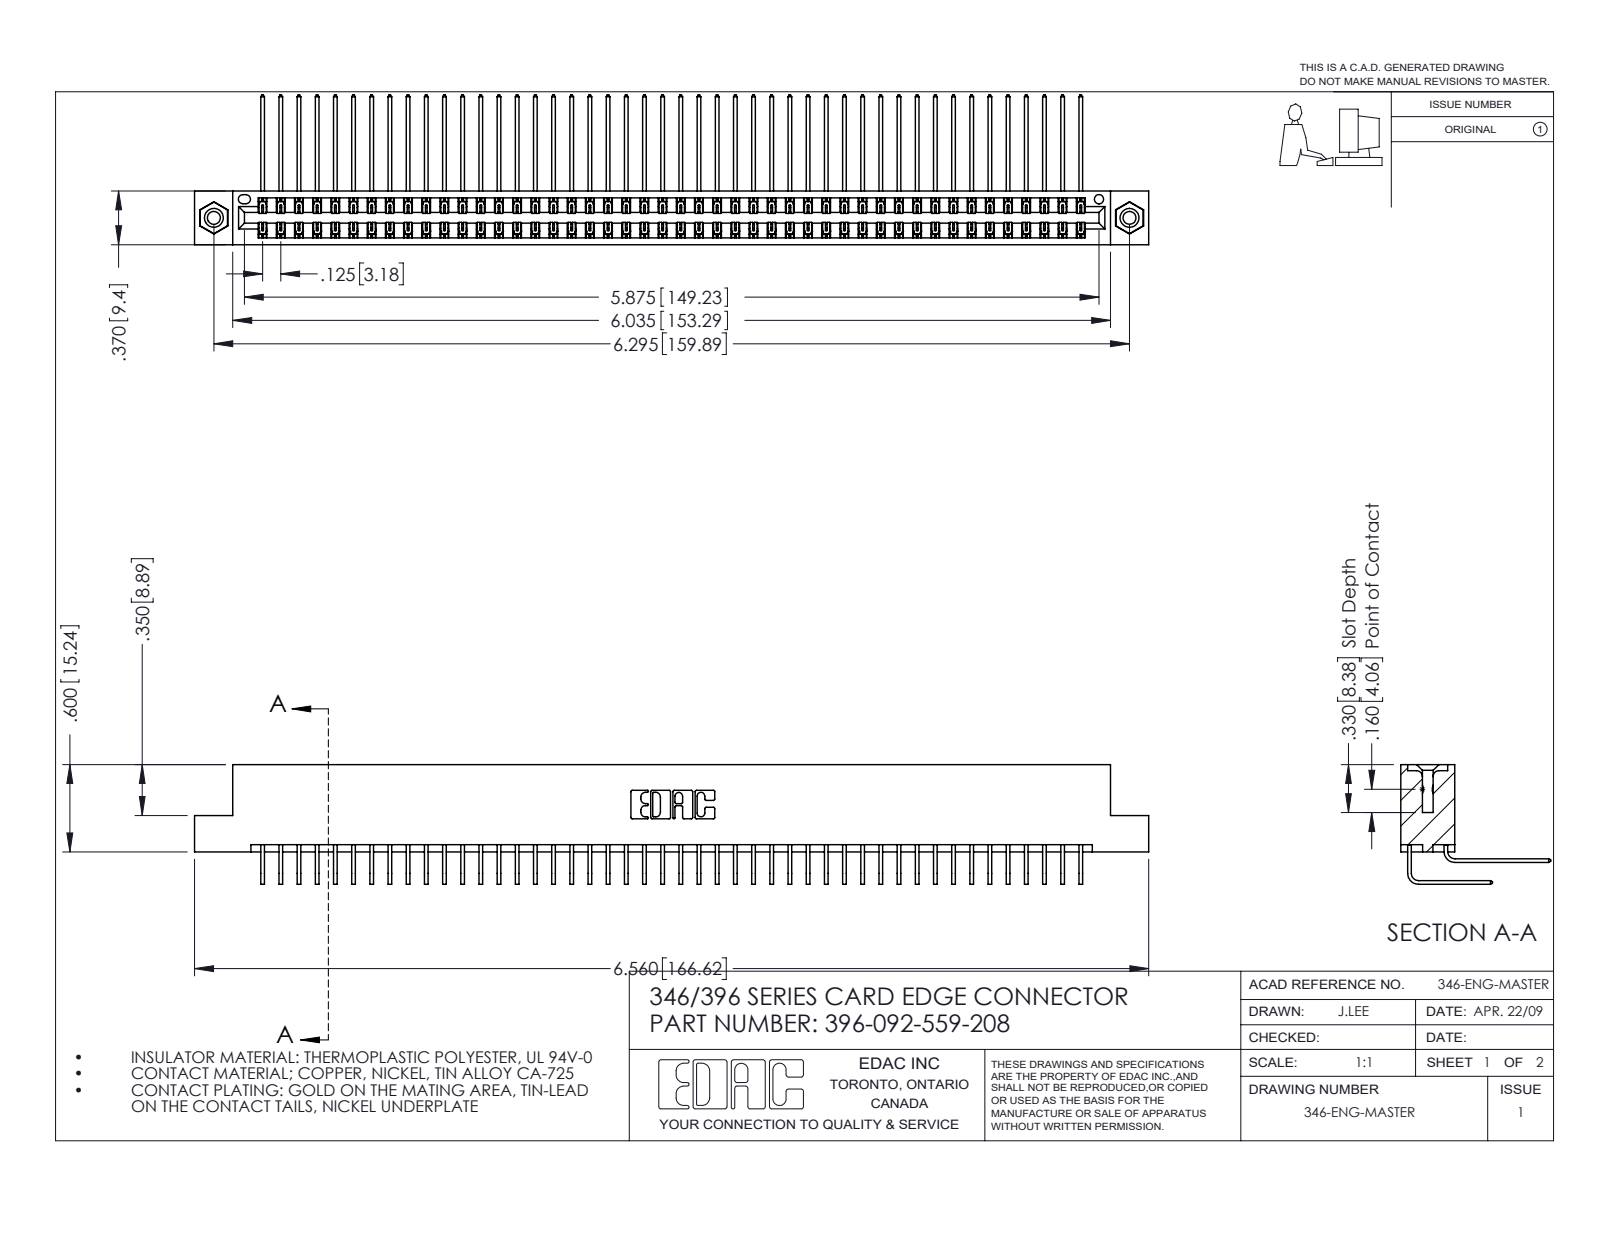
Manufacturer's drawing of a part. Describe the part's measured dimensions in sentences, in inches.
The part is named "345-250-001_345-250-003-102; 345-292-001_558 559 Tail - 1; 346 Part_Flush Mounting Lugs - 0.156 Dia-TI; 345-292-001_559 Tail - 2 (+1 more)". Its 3-D file was written by "SolidWorks 2016 (CONFIG_CONTROL_DESIGN)". It is 95 solids with 5150 faces: 3512 planar, 1622 cylindrical and 16 other. Overall it measures 6.56 by 1.03 by 0.823 inches. Its volume is 1.025 cubic inches and its surface area 39.88 square inches. Round holes: 2 of diameter 0.089, 2 of diameter 0.125, 2 of diameter 0.156, 1 of diameter 0.064. Round bosses or shafts: 2 of diameter 0.155. Partial cylindrical surfaces (rounded edges, fillets, slot ends): 138 of radius 0.006, 22 of radius 0.01, 6 of radius 0.007, 6 of radius 0.031, 3 of radius 0.026, 2 of radius 0.014, 2 of radius 0.022, 2 of radius 0.024. The main face-to-face distances are 0.048, 0.322, 0.025, 0.37, 0.25, 0.072, 0.298, 0.275, 0.148, 0.222. The hole center spacings are 0.246, 6.086, 6.295.
